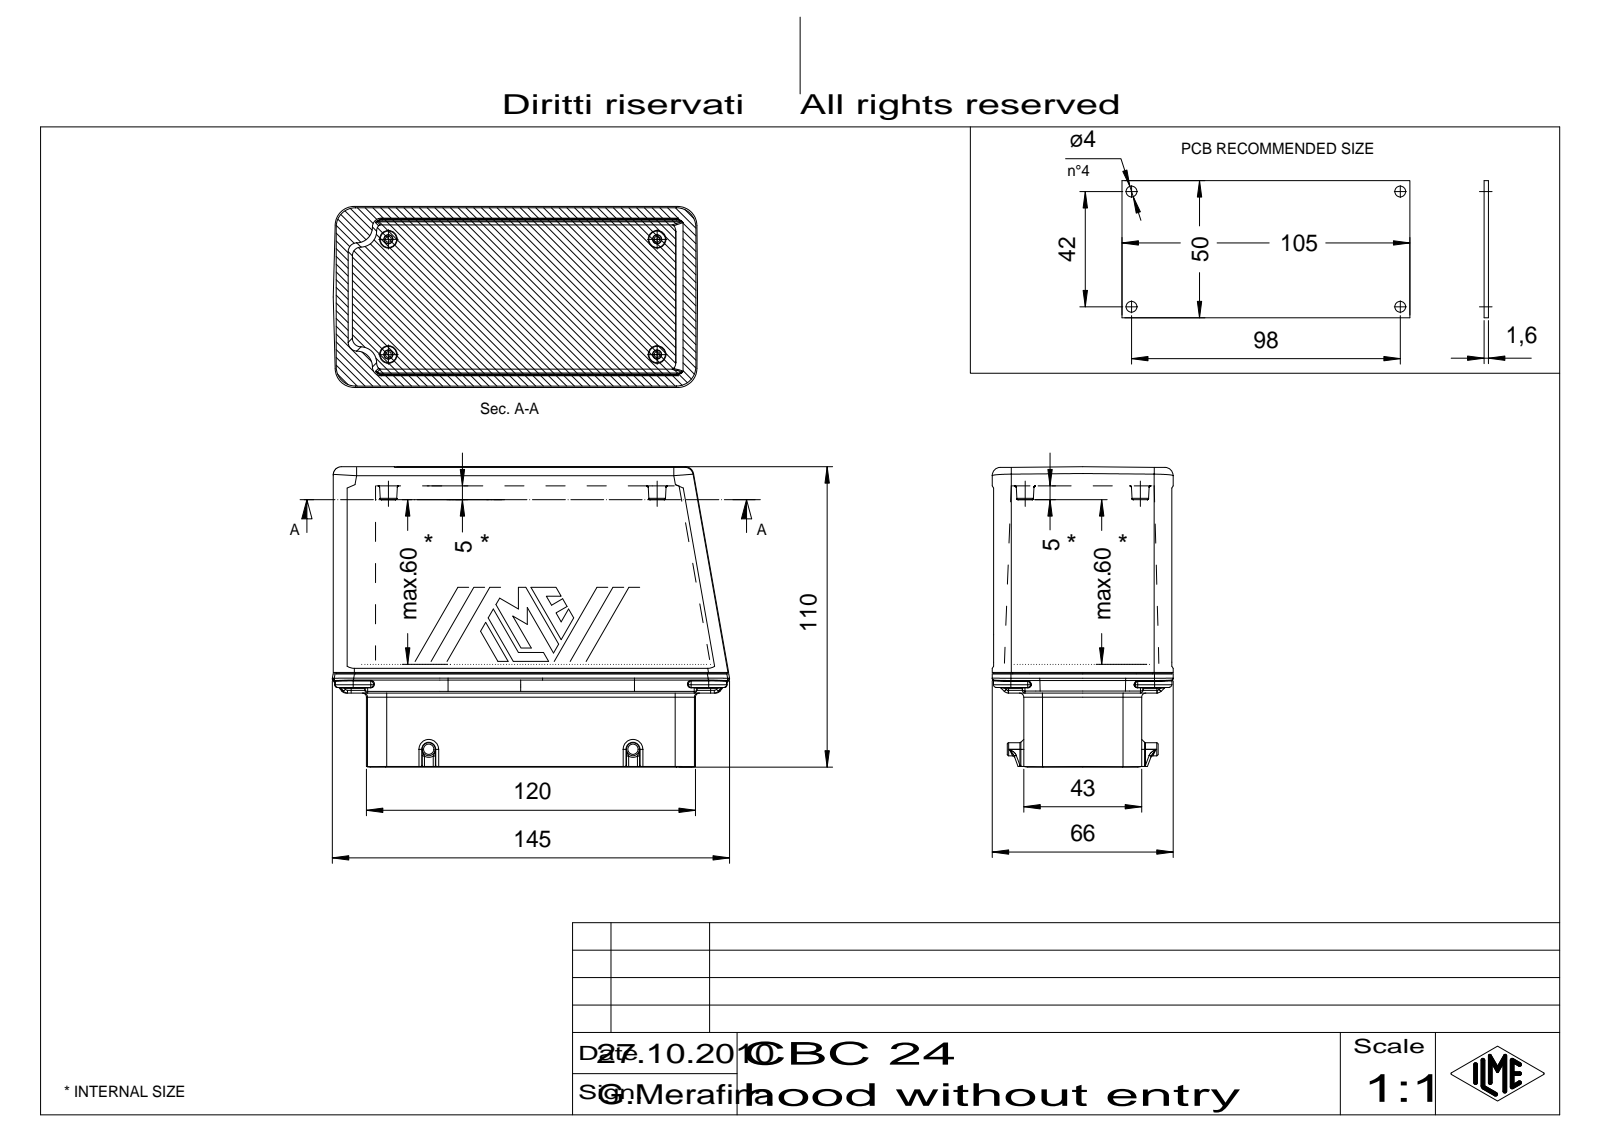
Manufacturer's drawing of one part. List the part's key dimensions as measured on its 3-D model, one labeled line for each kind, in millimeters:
Part name (STEP PRODUCT): 53848
STEP written by: CoCreate Modeling 16.00A 16-Aug-2008 (C) Parametric Technology GmbH (AUTOMOTIVE_DESIGN)
Units: millimetres
Bodies: 1 solid, 687 faces (371 planar, 112 cylindrical, 204 other)
Overall size (bounding box): 143.75 × 108.97 × 66.01
Volume: 757 151 mm³ · Surface area: 67 594 mm²
Round bosses / shafts (diameter × count): ⌀4.8 ×2
Partial cylindrical surfaces — rounded edges, fillets, slot ends (radius × count): R1 ×40, R7 ×12, R0.5 ×8, R1.5 ×6, R3 ×6, R0.3 ×4, R4.2 ×4, R5 ×4
Main face-to-face distances: 65.01, 82.21, 0.4, 65.41, 11, 54.01, 54, 43, 11.01, 54.41
